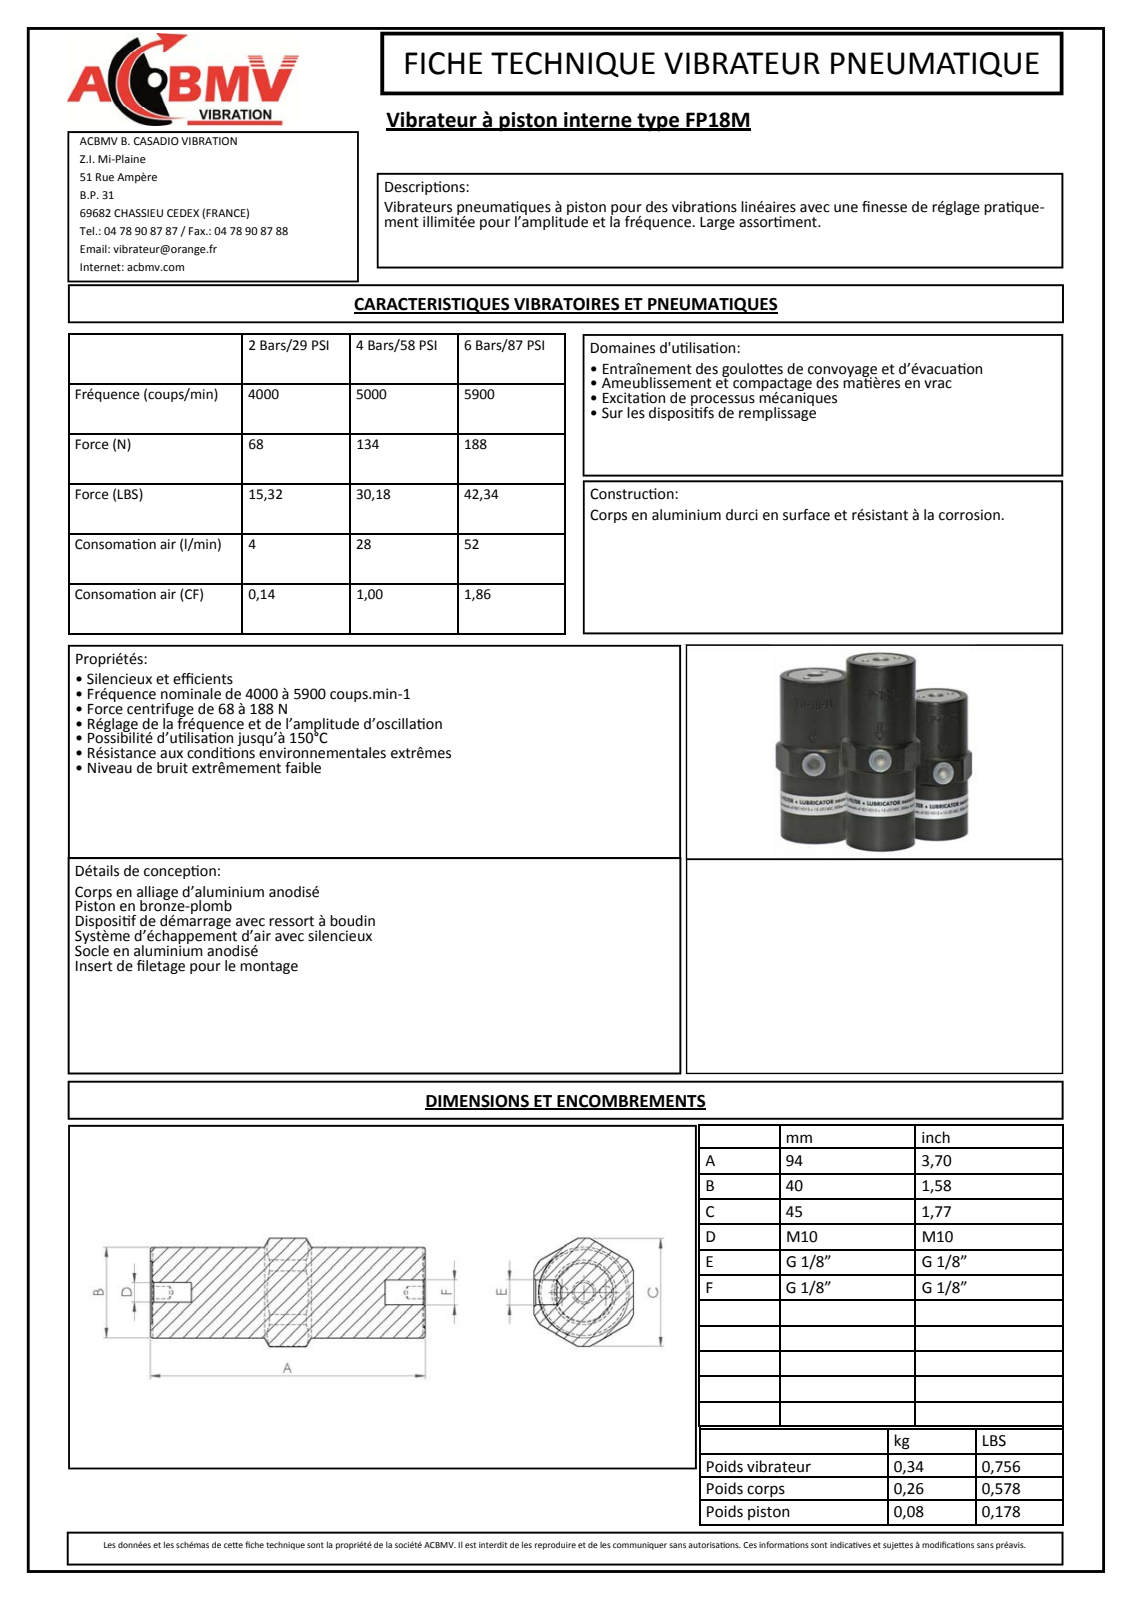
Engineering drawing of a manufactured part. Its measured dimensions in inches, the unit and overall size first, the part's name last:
Units: inches
Overall size (bounding box): 3.701 × 1.776 × 1.654
Round holes (diameter × count): ⌀0.165 ×2, ⌀0.337 ×2, ⌀0.33 ×1
Round bosses / shafts (diameter × count): ⌀1.575 ×1
Partial cylindrical surfaces — rounded edges, fillets, slot ends (radius × count): R0.433 ×1, R0.78 ×1, R0.791 ×1, R0.791 ×1, R0.888 ×1
Main face-to-face distances: 1.654, 3.681, 0.02, 3.701, 3.083, 3.063, 0.618, 0.63, 0.61, 2.453
Hole centre spacings: 0.394, 0.787
Volume: 7.231 in³ · Surface area: 25.23 in²
Bodies: 1 solid, 446 faces (177 planar, 58 cylindrical, 211 other)
Part name (STEP PRODUCT): 9018-20-M
STEP written by: Autodesk Inventor 2011 (CONFIG_CONTROL_DESIGN)
